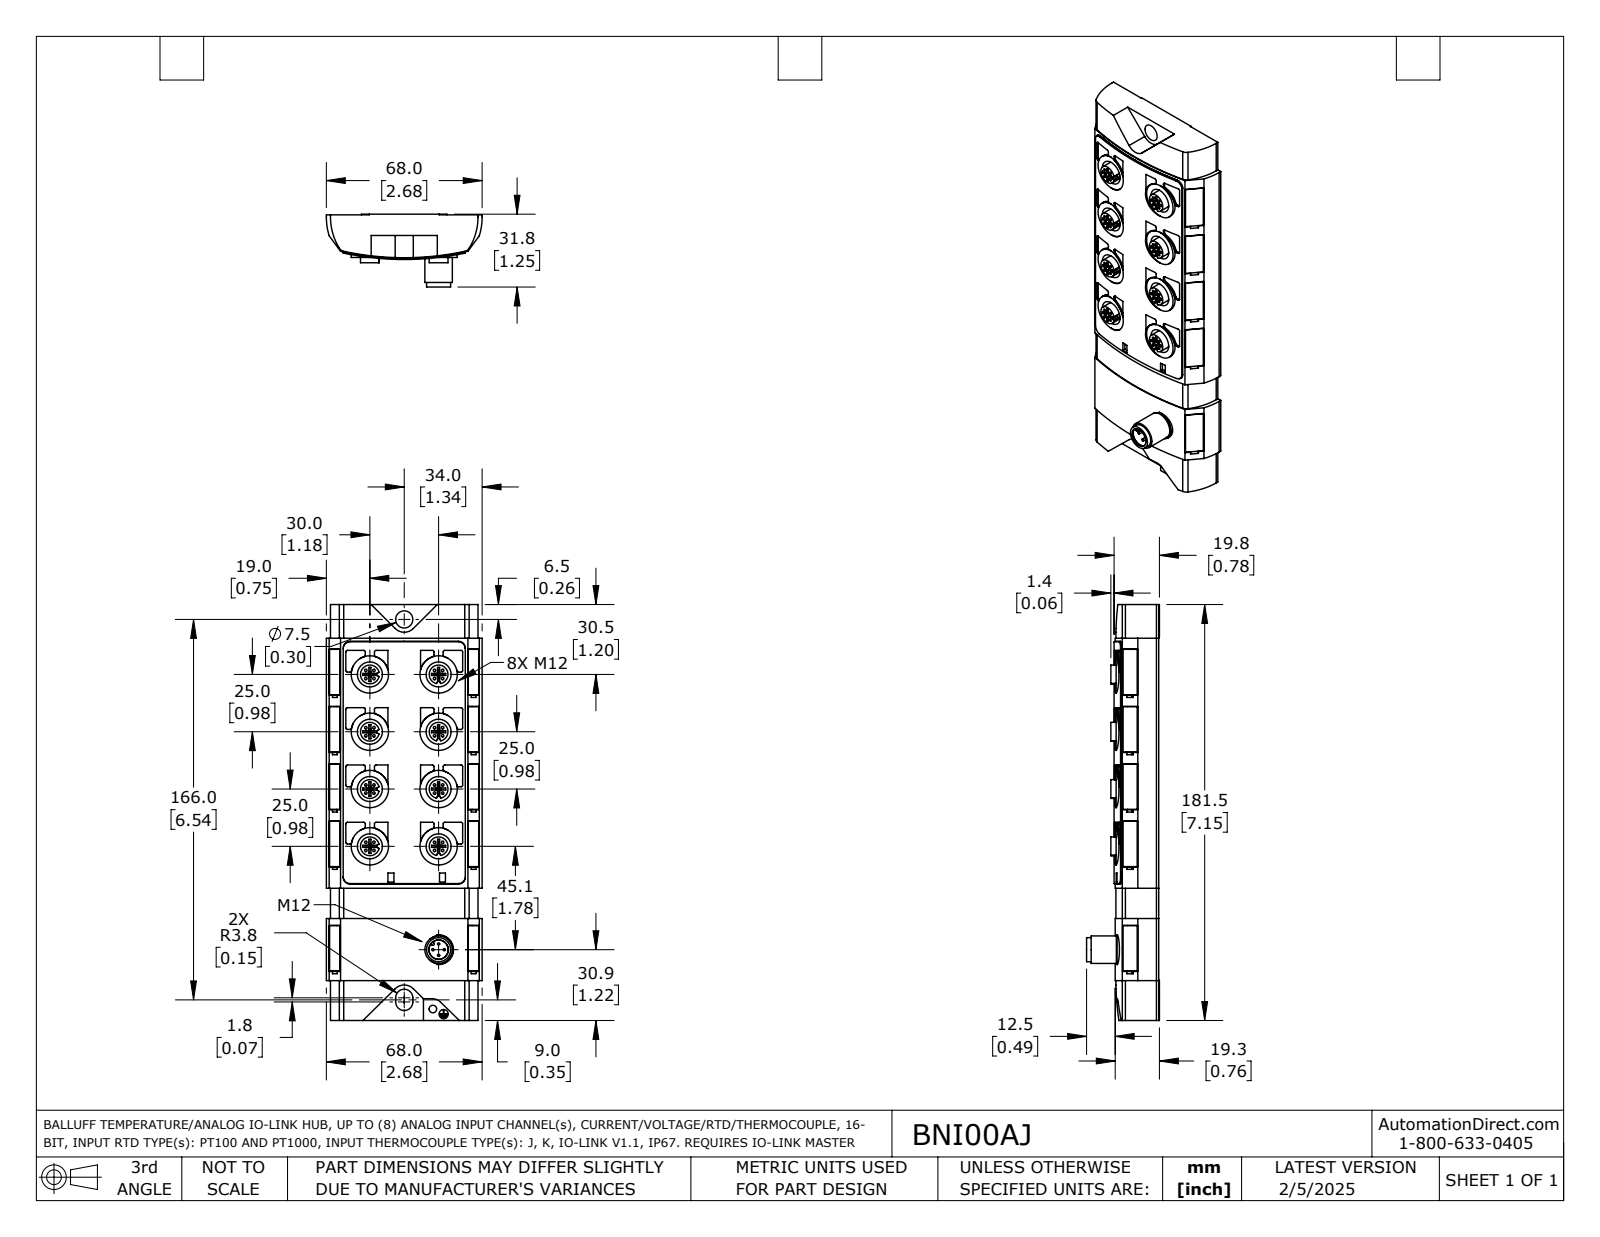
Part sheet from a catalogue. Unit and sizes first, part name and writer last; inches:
Units: inches
Overall size (bounding box): 7.146 × 2.677 × 1.252
Round holes (diameter × count): ⌀0.043 ×40, ⌀0.43 ×8, ⌀0.642 ×4, ⌀0.13 ×1, ⌀0.157 ×1, ⌀0.295 ×1, ⌀0.331 ×1, ⌀0.335 ×1
Round bosses / shafts (diameter × count): ⌀0.323 ×8, ⌀0.642 ×4, ⌀0.039 ×4, ⌀0.472 ×1, ⌀0.413 ×1
Partial cylindrical surfaces — rounded edges, fillets, slot ends (radius × count): R0.028 ×80, R0.031 ×40, R0.008 ×16, R0.321 ×8, R0.118 ×7, R0.117 ×3, R0.148 ×2, R0.22 ×2
Main face-to-face distances: 0.315, 0.732, 0.319, 0.311, 7.146, 0.744, 0.354, 0.551, 0.539, 0.193
Hole centre spacings: 0.098, 0.139, 0.984, 0.917, 1.056, 1.537, 2.296, 0.994
Volume: 12.18 in³ · Surface area: 66.18 in²
Bodies: 1 solid, 855 faces (473 planar, 380 cylindrical, 2 other)
Part name (STEP PRODUCT): BNI00AJ
STEP written by: SolidWorks 2021 (AUTOMOTIVE_DESIGN)
